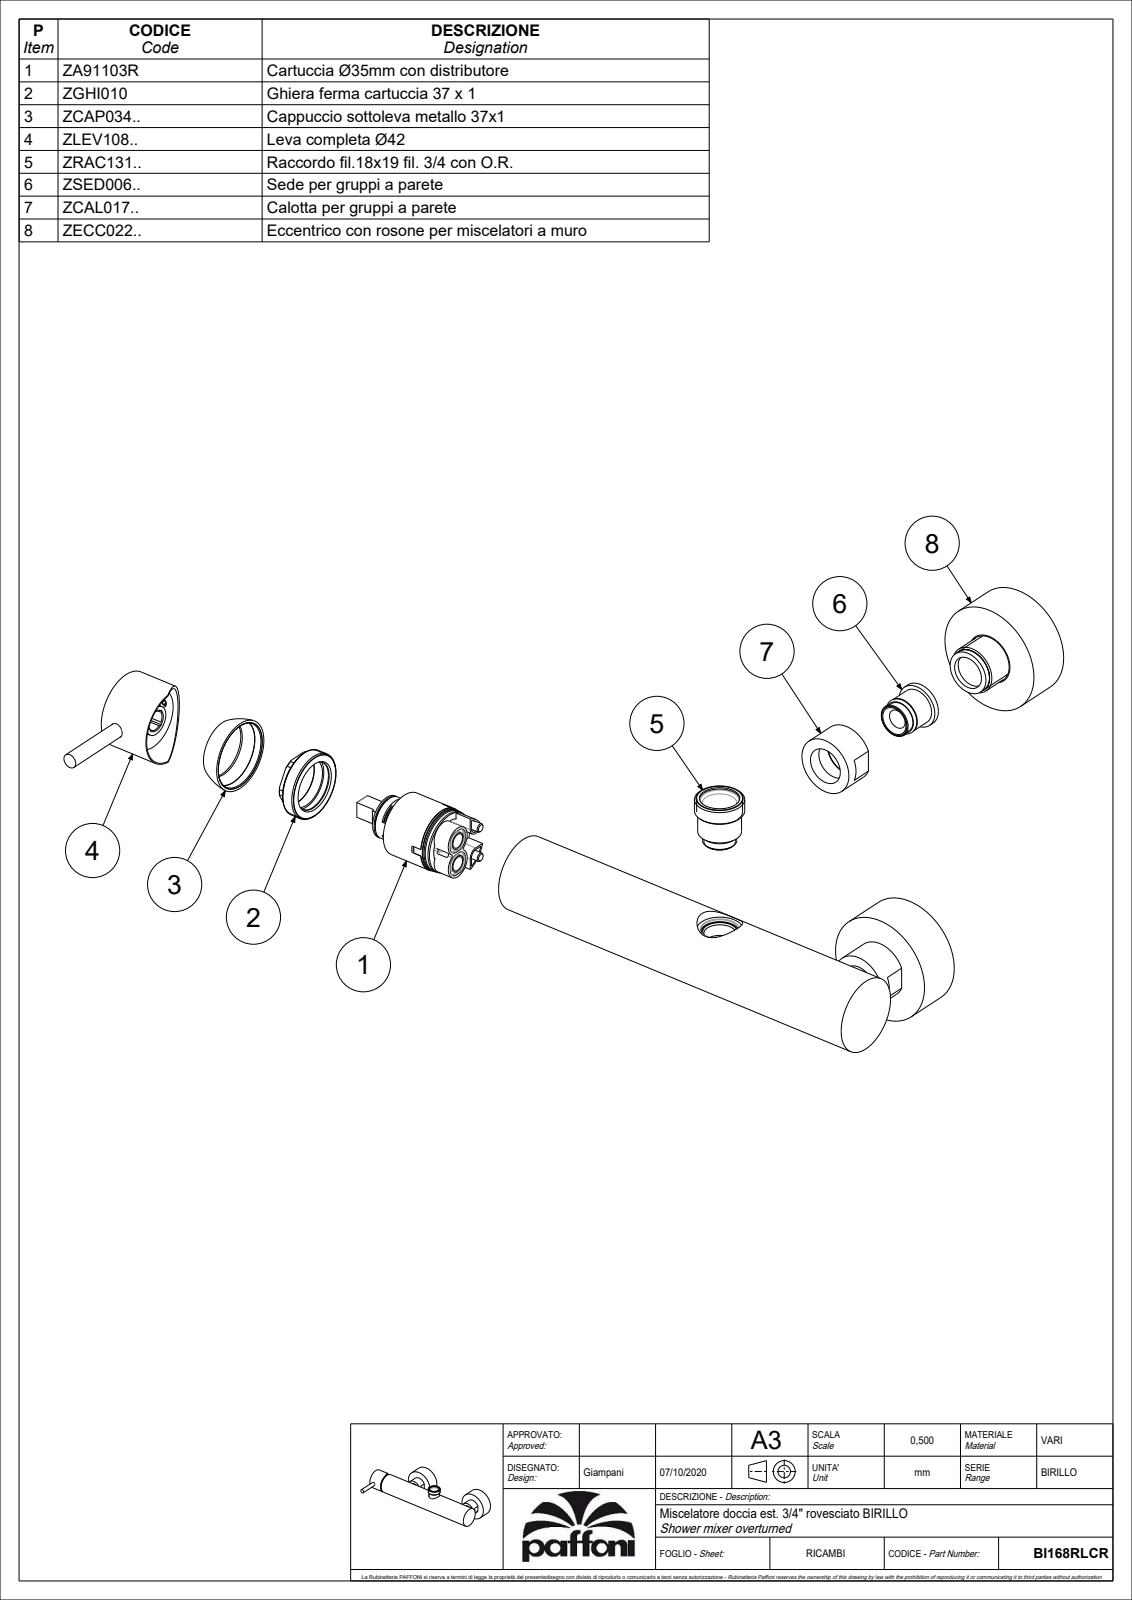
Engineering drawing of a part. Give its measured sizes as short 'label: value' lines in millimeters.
name: BI168RLCR
written by: CREO PARAMETRIC BY PTC INC, 2020044 (CONFIG_CONTROL_DESIGN)
unit: mm
bodies: 1 solid, 1242 faces (686 planar, 347 cylindrical, 209 other)
size: 268.91 × 125.12 × 66
volume: 352 092 mm³; area: 117 103 mm²
holes: 6× ⌀7.5, 3× ⌀8, 3× ⌀9, 3× ⌀12, 3× ⌀16.7, 2× ⌀4, 2× ⌀10.5, 2× ⌀18, 2× ⌀20, 2× ⌀24.5, 2× ⌀55, 1× ⌀3
bosses: 2× ⌀59.5, 2× ⌀41.5, 2× ⌀31.5, 2× ⌀24, 2× ⌀19.7, 1× ⌀35, 1× ⌀34.8, 1× ⌀33.8
rounds: 44× R0.5, 11× R0.15, 9× R0.3, 4× R1, 4× R7, 2× R4.5, 2× R7.95, 1× R5.3
face distances: 4.7, 18, 22.7, 20, 24.7, 42.7, 10, 31.9, 3, 2.5
hole spacings: 14, 0.71, 0.9, 8.46, 8.5, 8.51, 8.56, 8.6
